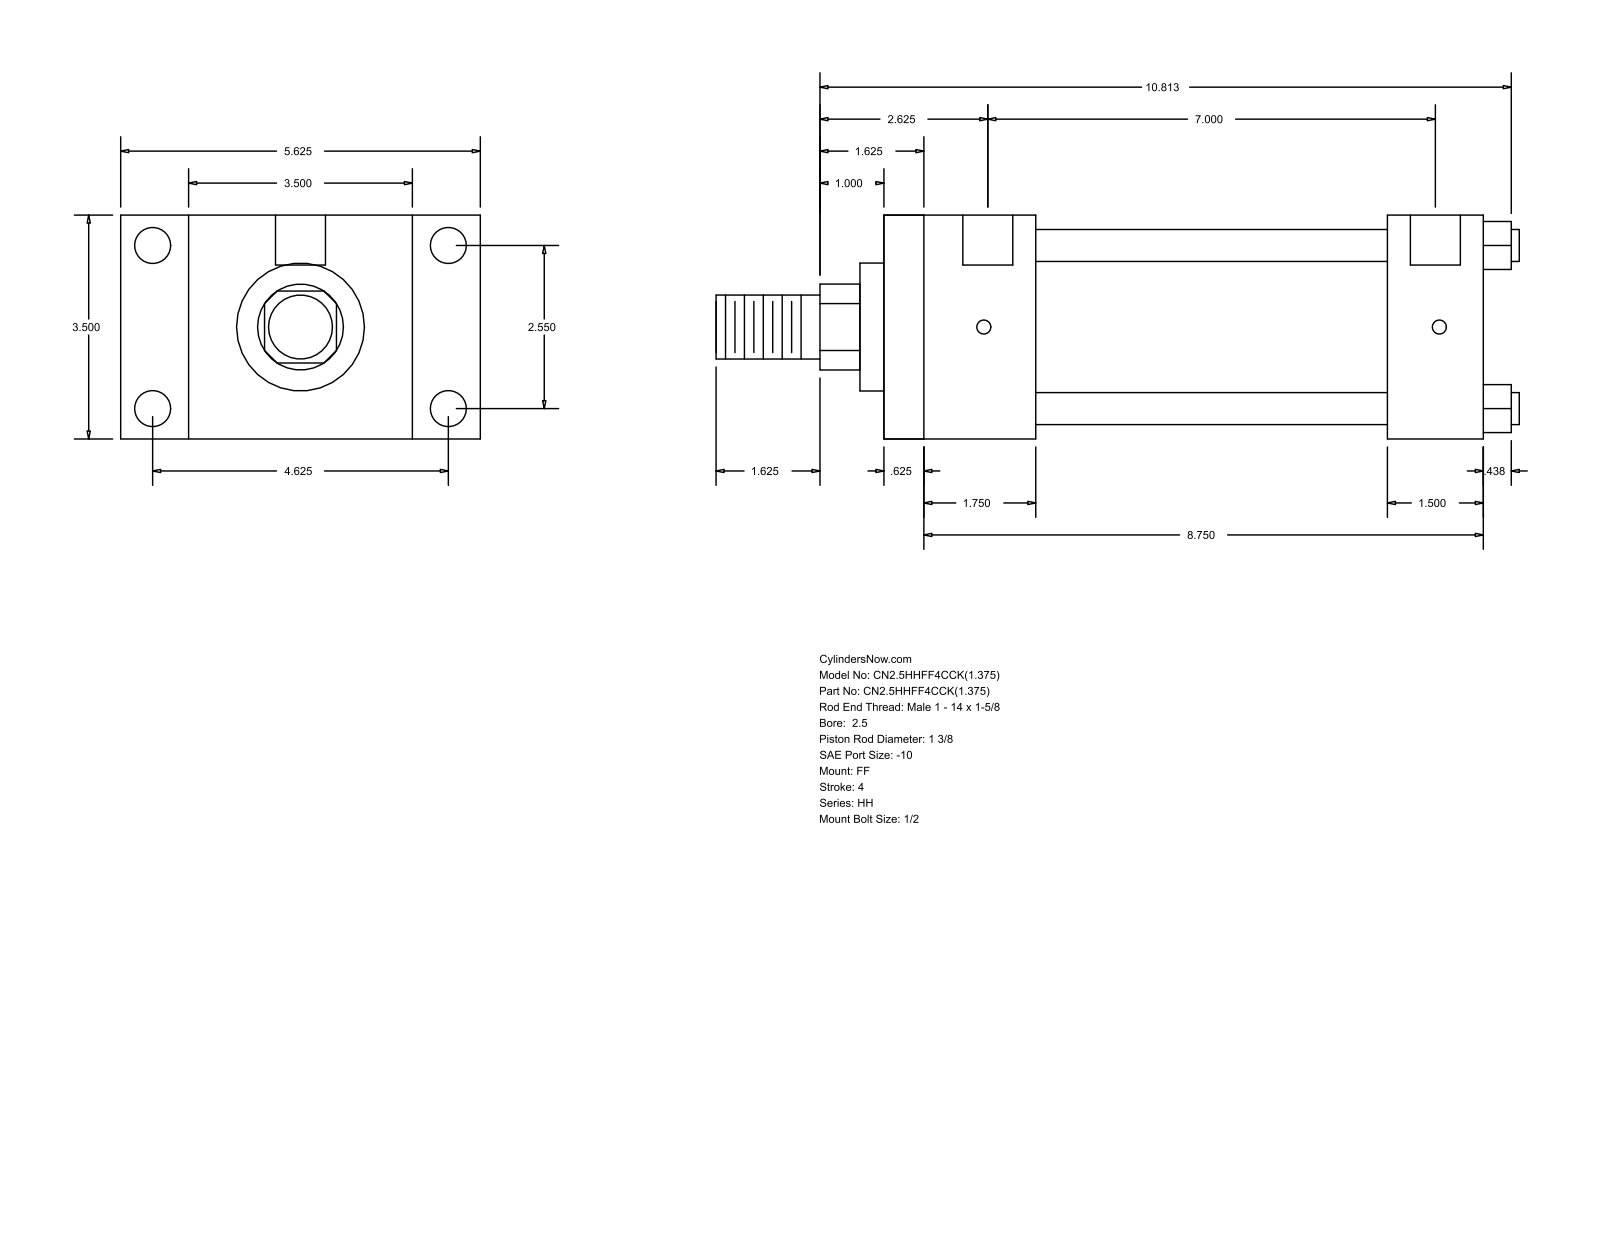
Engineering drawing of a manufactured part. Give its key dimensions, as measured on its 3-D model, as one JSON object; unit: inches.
{"part_name": "HH_FF__0250_1.375", "step_written_by": "GSSL Pune (CONFIG_CONTROL_DESIGN)", "units": "inches", "bodies": {"solids": 0, "faces": 92, "planar": 64, "cylindrical": 28, "other": 0}, "overall_size": [12.563, 5.625, 3.5], "round_holes": [[0.219, 4], [0.563, 4], [0.781, 2]], "round_bosses_or_shafts": [[0.5, 4], [2.875, 1], [2, 1], [1.375, 1], [1, 1]], "partial_cylinders_radius": [[0.672, 1]], "face_to_face_distances": [3.5, 9.375, 0.625, 8.75, 2.375, 1.75, 7, 7.875, 7.25, 5.5], "hole_center_spacings": [2.55, 4.625, 5.281, 7.125, 0.062, 0.063, 7, 7.062]}
